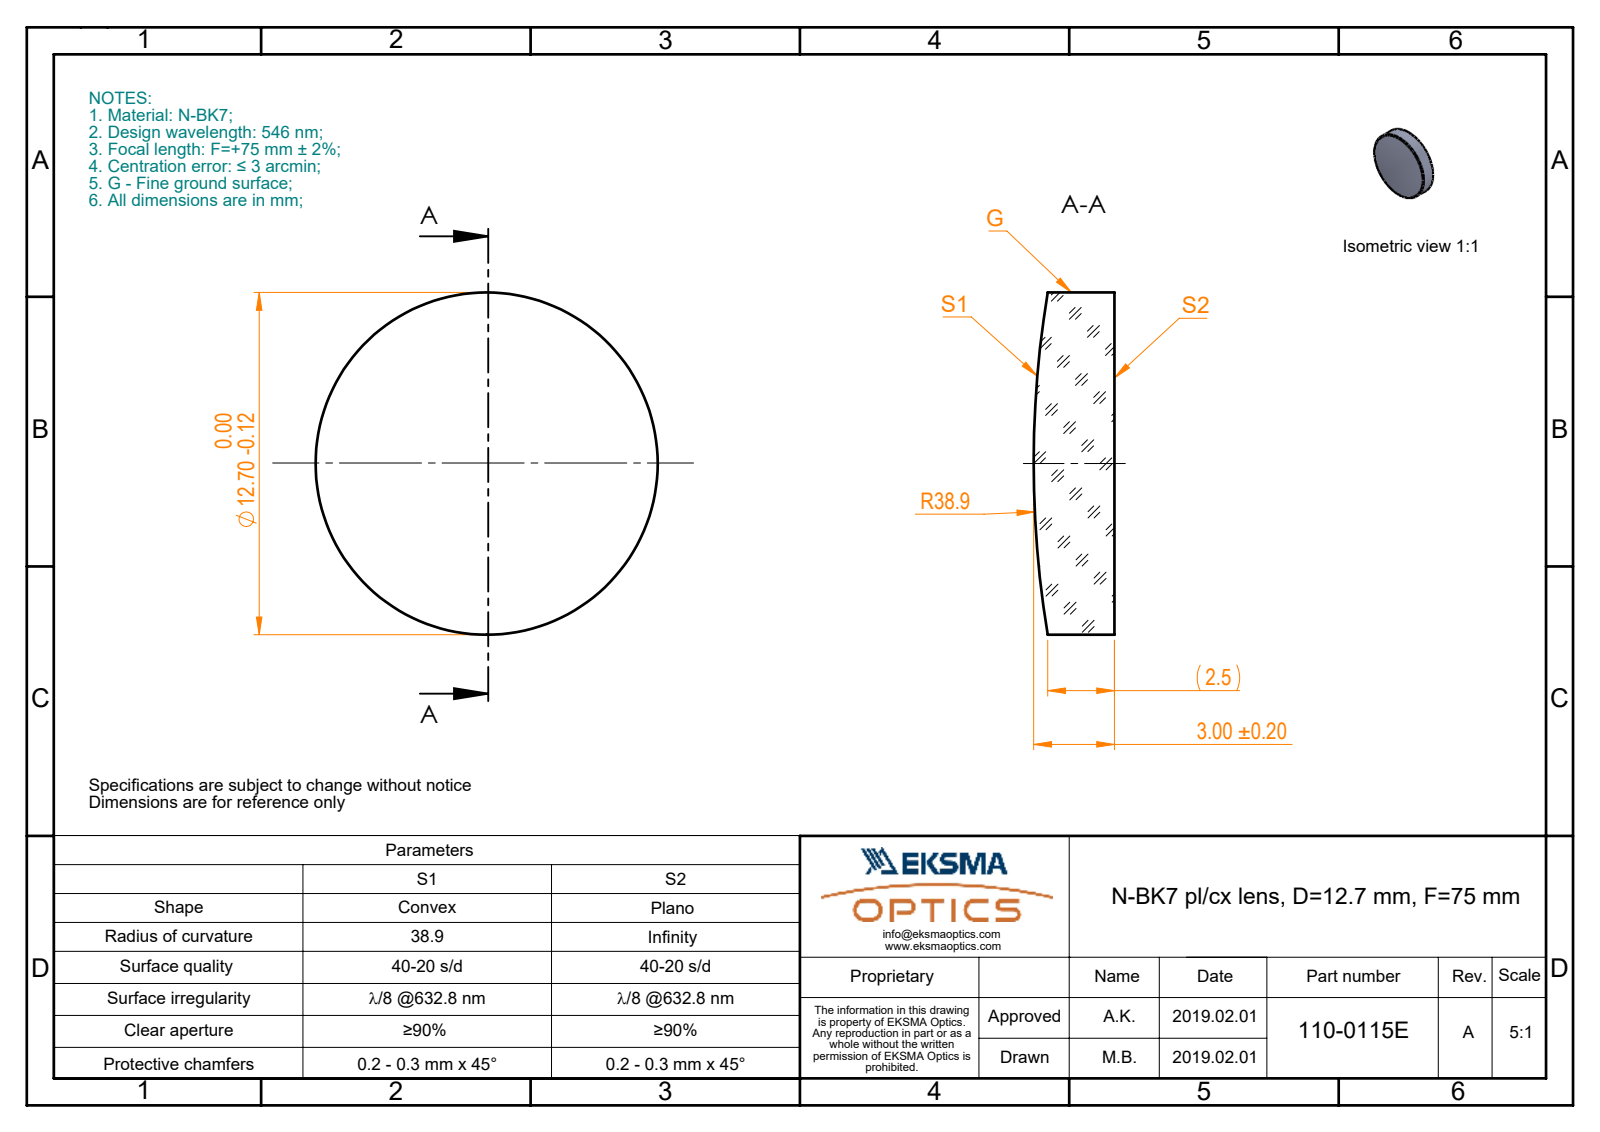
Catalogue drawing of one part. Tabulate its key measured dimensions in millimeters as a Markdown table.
| quantity | value |
| --- | --- |
| part name | 110-0115E BK7 pl-cx 12.7 F75 |
| STEP written by | SolidWorks 2017 (CONFIG_CONTROL_DESIGN) |
| units | millimeters |
| bodies | 1 solid, 5 faces (1 planar, 2 cylindrical, 2 other) |
| overall size | 12.7 × 12.7 × 3 |
| volume | 347 mm³ |
| surface area | 353 mm² |
| round bosses / shafts (diameter × count) | 12.7 × 1 |
